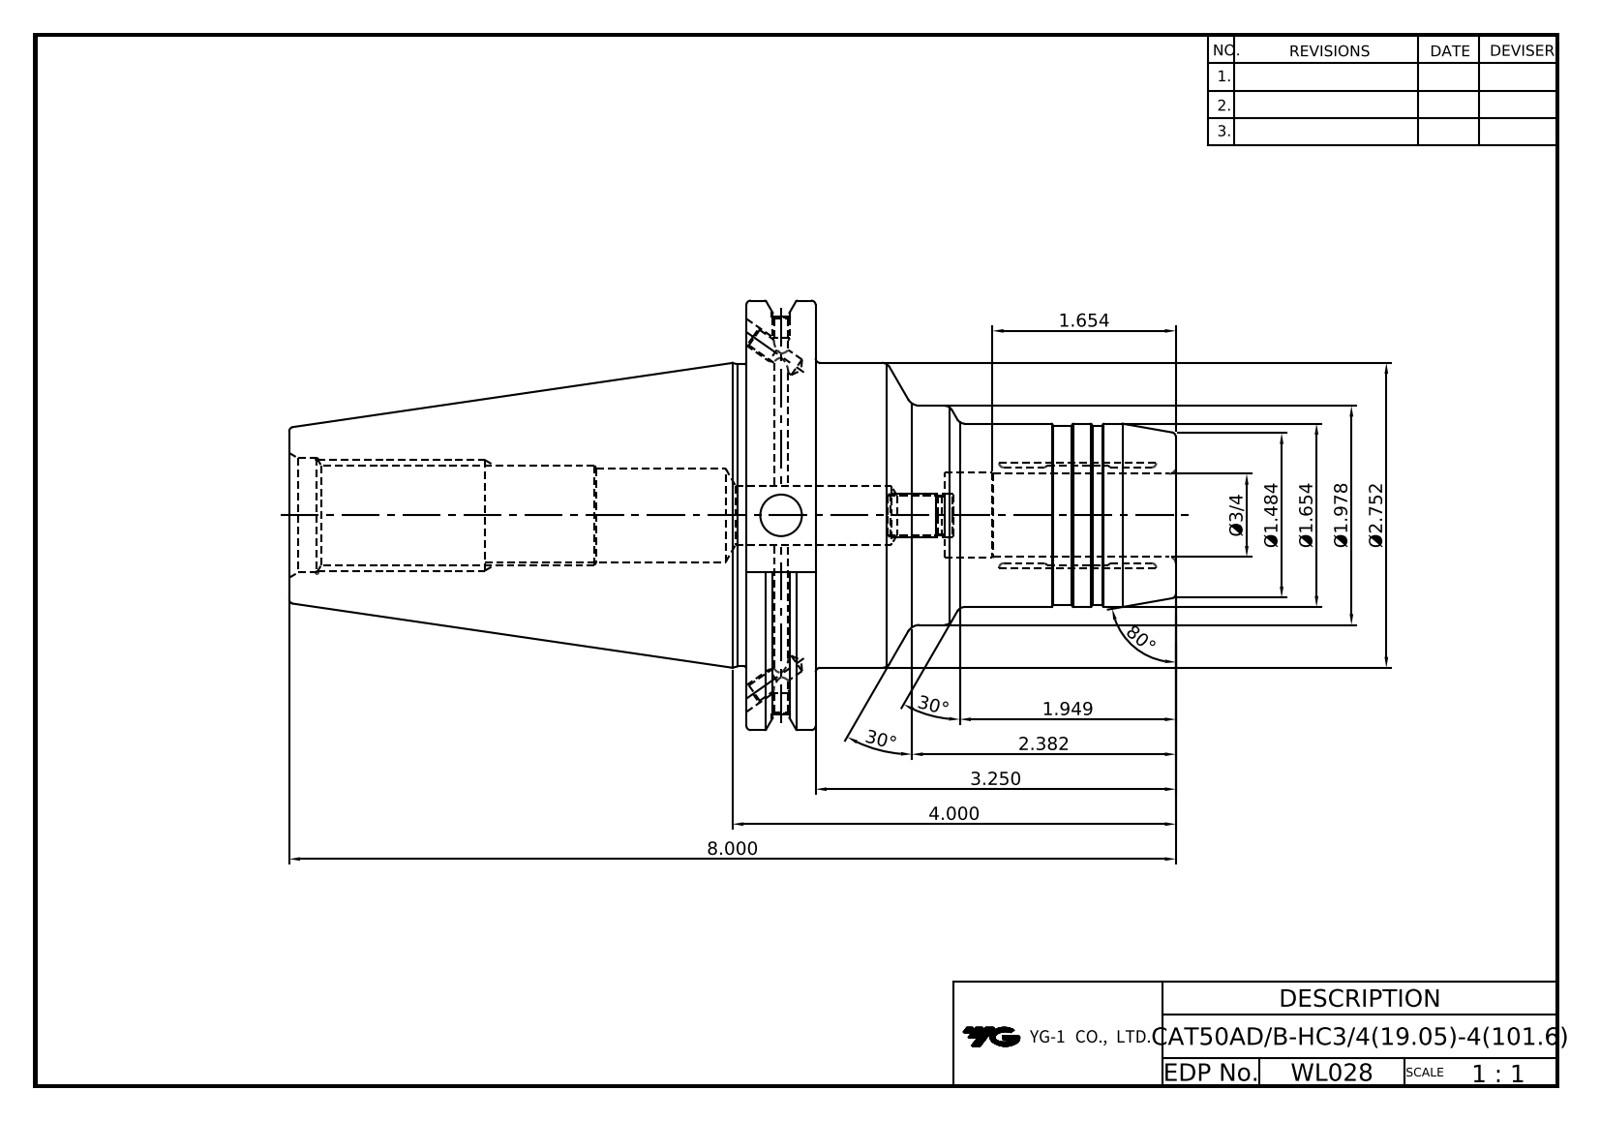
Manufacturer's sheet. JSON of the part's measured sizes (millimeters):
{"part_name": "LO-CAT50ADB-HC19.05-101.6", "step_written_by": "Autodesk Inventor 2020 (AUTOMOTIVE_DESIGN)", "units": "millimeters", "bodies": {"solids": 1, "faces": 112, "planar": 37, "cylindrical": 34, "other": 41}, "overall_size": [203.2, 98.42, 94.69], "volume_mm3": 472235, "surface_area_mm2": 60215, "round_holes": [[3.24, 2], [4.13, 2], [4.2, 2], [5, 2], [8.92, 1], [9.53, 1], [13.5, 1], [19.05, 1], [19.4, 1], [20.5, 1], [21.97, 1], [26.2, 1]], "round_bosses_or_shafts": [[98.42, 1], [91.29, 1], [69.9, 1], [69.25, 1], [50.25, 1], [42, 1], [41, 1]], "face_to_face_distances": [15.88, 98.43, 82.55, 104.77, 120.65, 203.2, 73.03, 25.9, 150.2, 45.43]}
